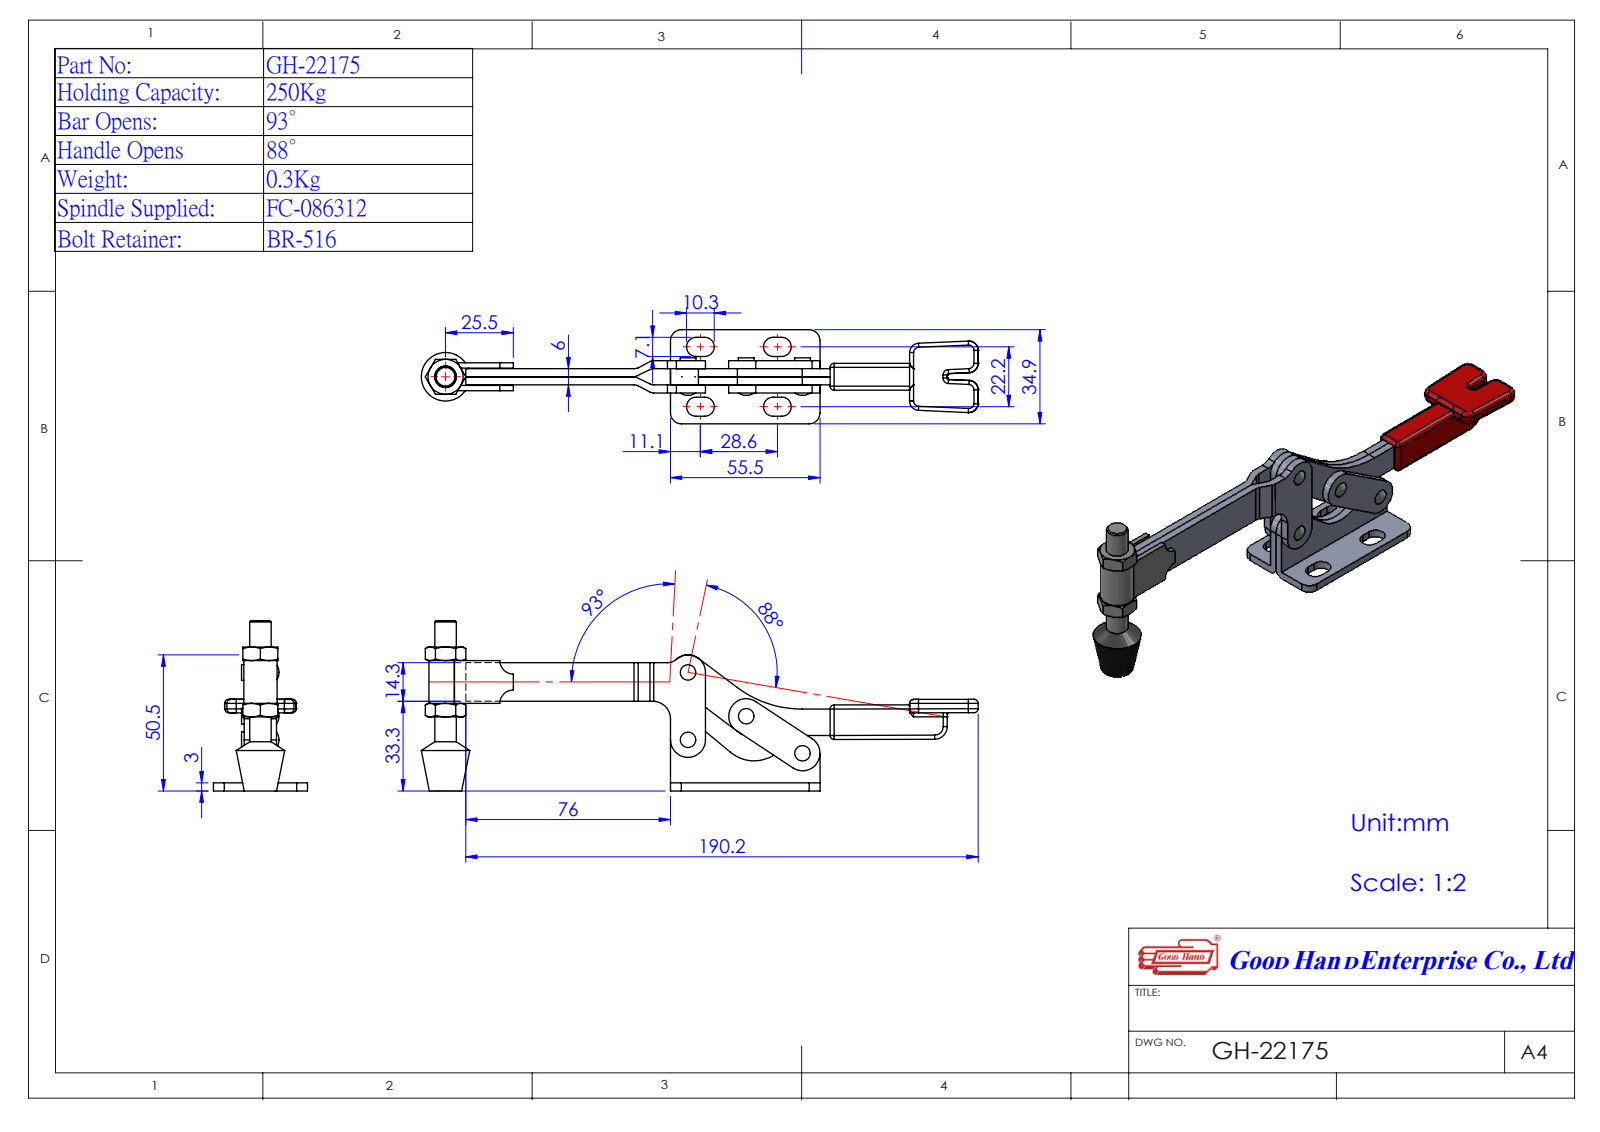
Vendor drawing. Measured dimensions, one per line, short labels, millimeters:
name: Group4^GH-22165(簡化); GH-22175(簡化); Group2^GH-22175(簡化); 12216501-1^GH-22175(簡化) (+2 more)
written by: SolidWorks 2016 (AUTOMOTIVE_DESIGN)
unit: mm
bodies: 6 solids, 288 faces (132 planar, 118 cylindrical, 38 other)
size: 208.09 × 63.2 × 34.9
volume: 43 549 mm³; area: 29 098 mm²
holes: 4× ⌀3.5, 2× ⌀4.83
bosses: 4× ⌀5.85, 1× ⌀13, 1× ⌀7.93
rounds: 8× R3.55, 6× R3.47, 4× R4, 4× R6.5, 3× R3, 3× R4.15, 2× R0.53, 2× R2.42
face distances: 3, 6, 9, 5, 1, 2, 11, 8, 12, 13
hole spacings: 25, 23.34, 27.05, 42.79, 52.02
